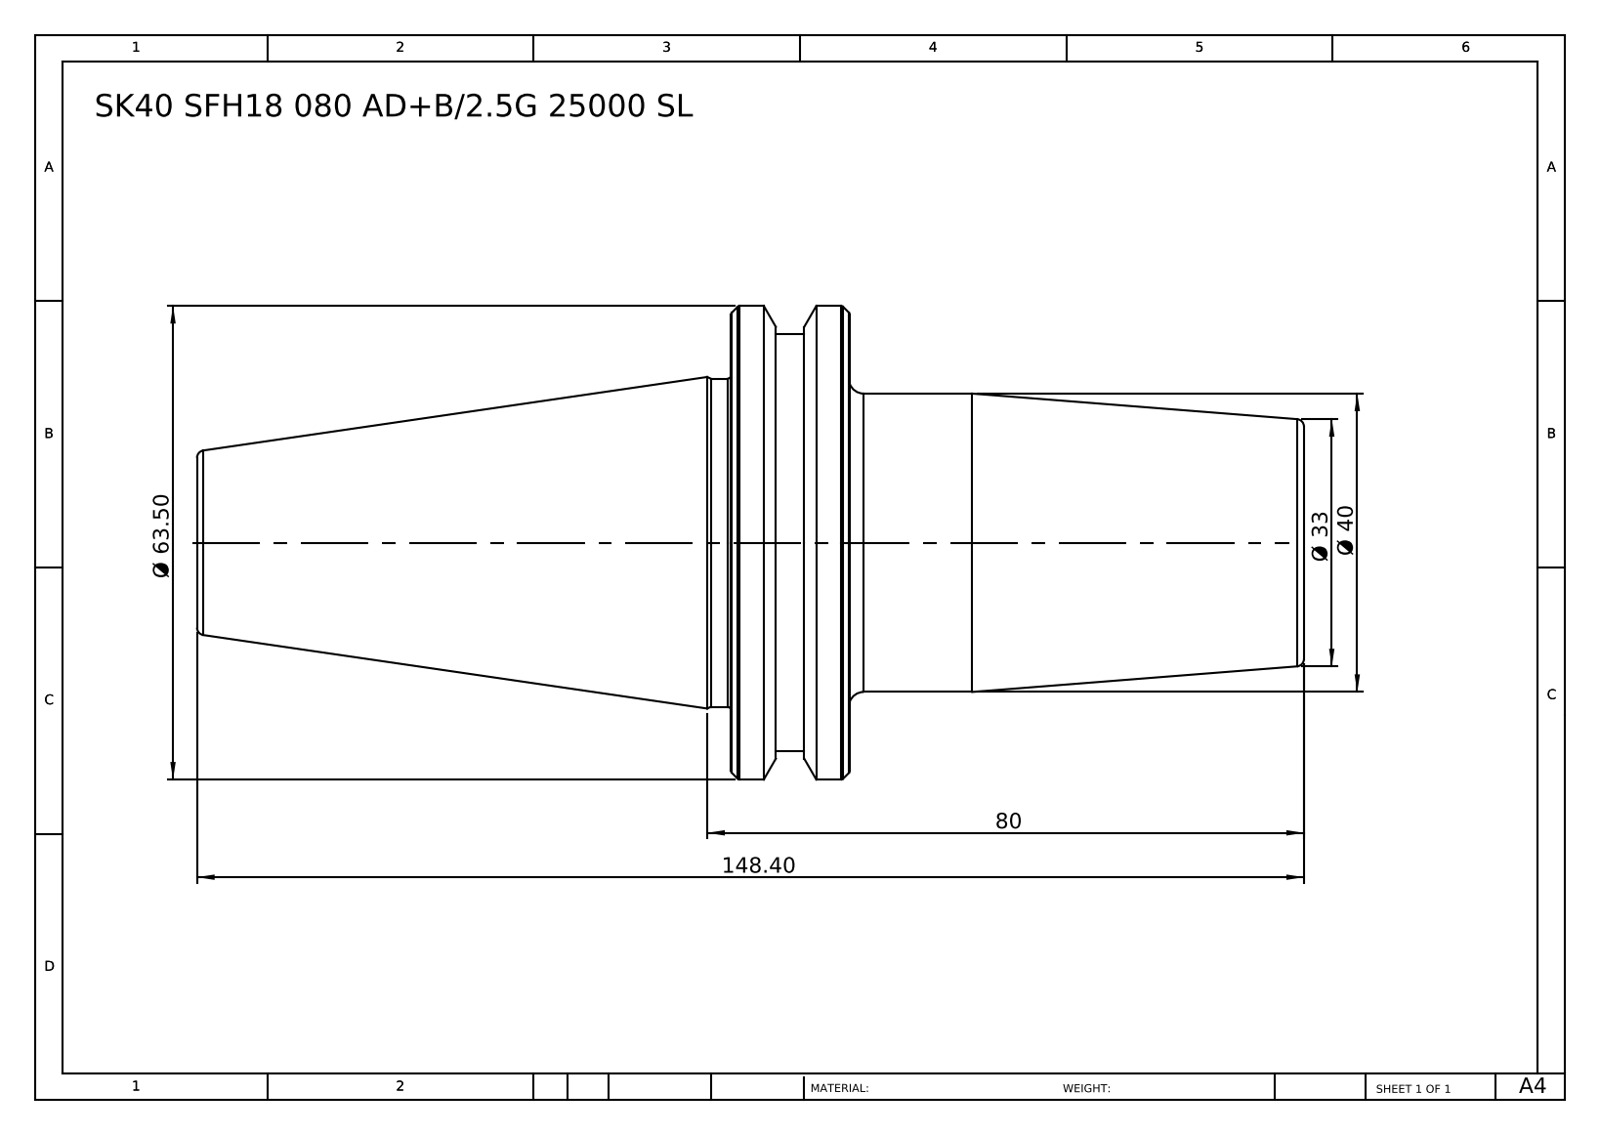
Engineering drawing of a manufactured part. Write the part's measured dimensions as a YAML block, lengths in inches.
part_name: "SK40 SFH18 80 AD+B-2.5G 25000 SL"
step_written_by: "SolidWorks 2014 (CONFIG_CONTROL_DESIGN)"
units: inches
bodies: {solids: 1, faces: 46, planar: 6, cylindrical: 10, other: 30}
overall_size: [5.843, 2.5, 2.5]
volume: 11.26
surface_area: 36.54
round_bosses_or_shafts:
  - {diameter: 2.5, count: 1}
  - {diameter: 2.205, count: 1}
  - {diameter: 1.732, count: 1}
  - {diameter: 1.575, count: 1}
face_to_face_distances: [0.626, 2.398, 3.024, 5.843, 3.445, 2.819, 2.638, 0.24, 0.386, 3.205]
